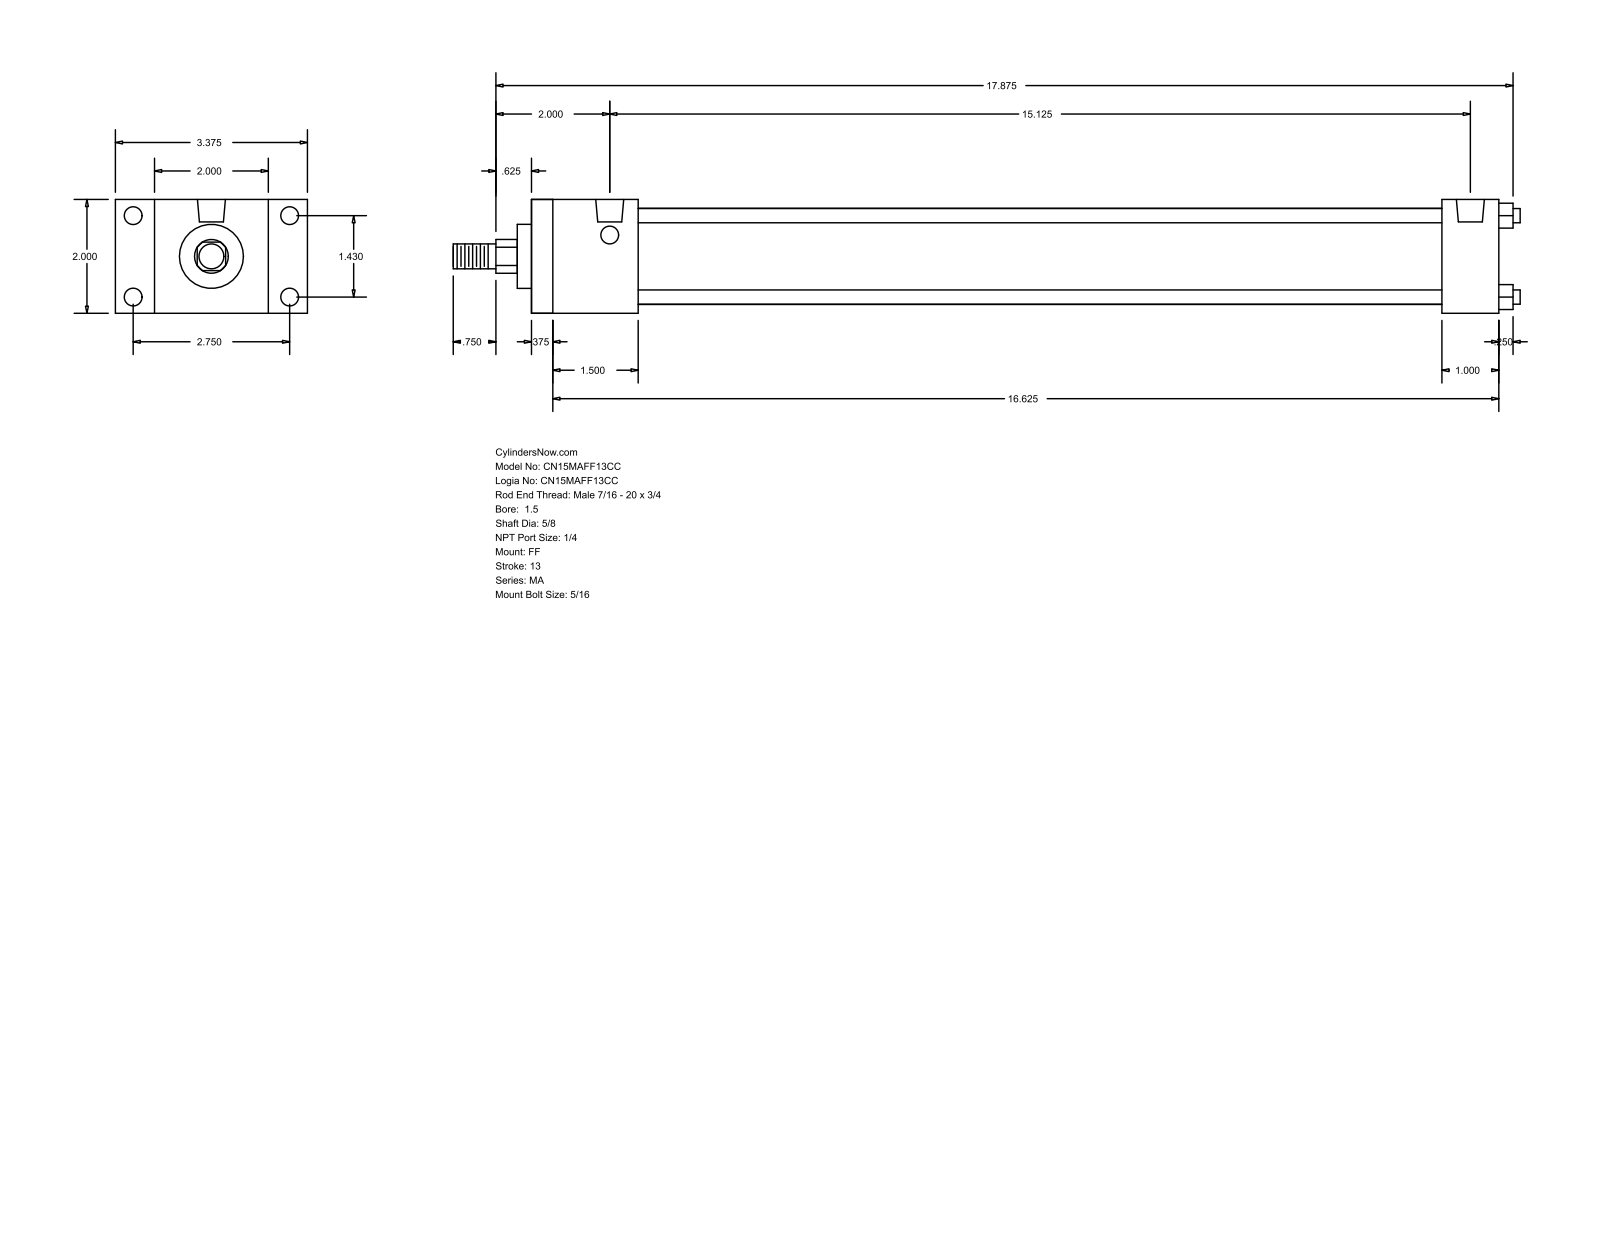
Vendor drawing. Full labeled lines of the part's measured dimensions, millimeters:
Part name (STEP PRODUCT): MA_FF__0150_0.625
STEP written by: GSSL Pune (CONFIG_CONTROL_DESIGN)
Units: millimetres
Bodies: 0 solids, 92 faces (64 planar, 28 cylindrical, 0 other)
Overall size (bounding box): 476.25 × 85.72 × 50.8
Round holes (diameter × count): ⌀7.94 ×8, ⌀12.49 ×2
Round bosses / shafts (diameter × count): ⌀6.35 ×4, ⌀42.93 ×1, ⌀28.57 ×1, ⌀15.88 ×1, ⌀11.11 ×1
Partial cylindrical surfaces — rounded edges, fillets, slot ends (radius × count): R7.54 ×1
Main face-to-face distances: 50.8, 431.8, 9.52, 422.28, 47.62, 406.39, 38.1, 396.87, 358.77, 384.18
Hole centre spacings: 36.32, 69.84, 78.72, 384.18
